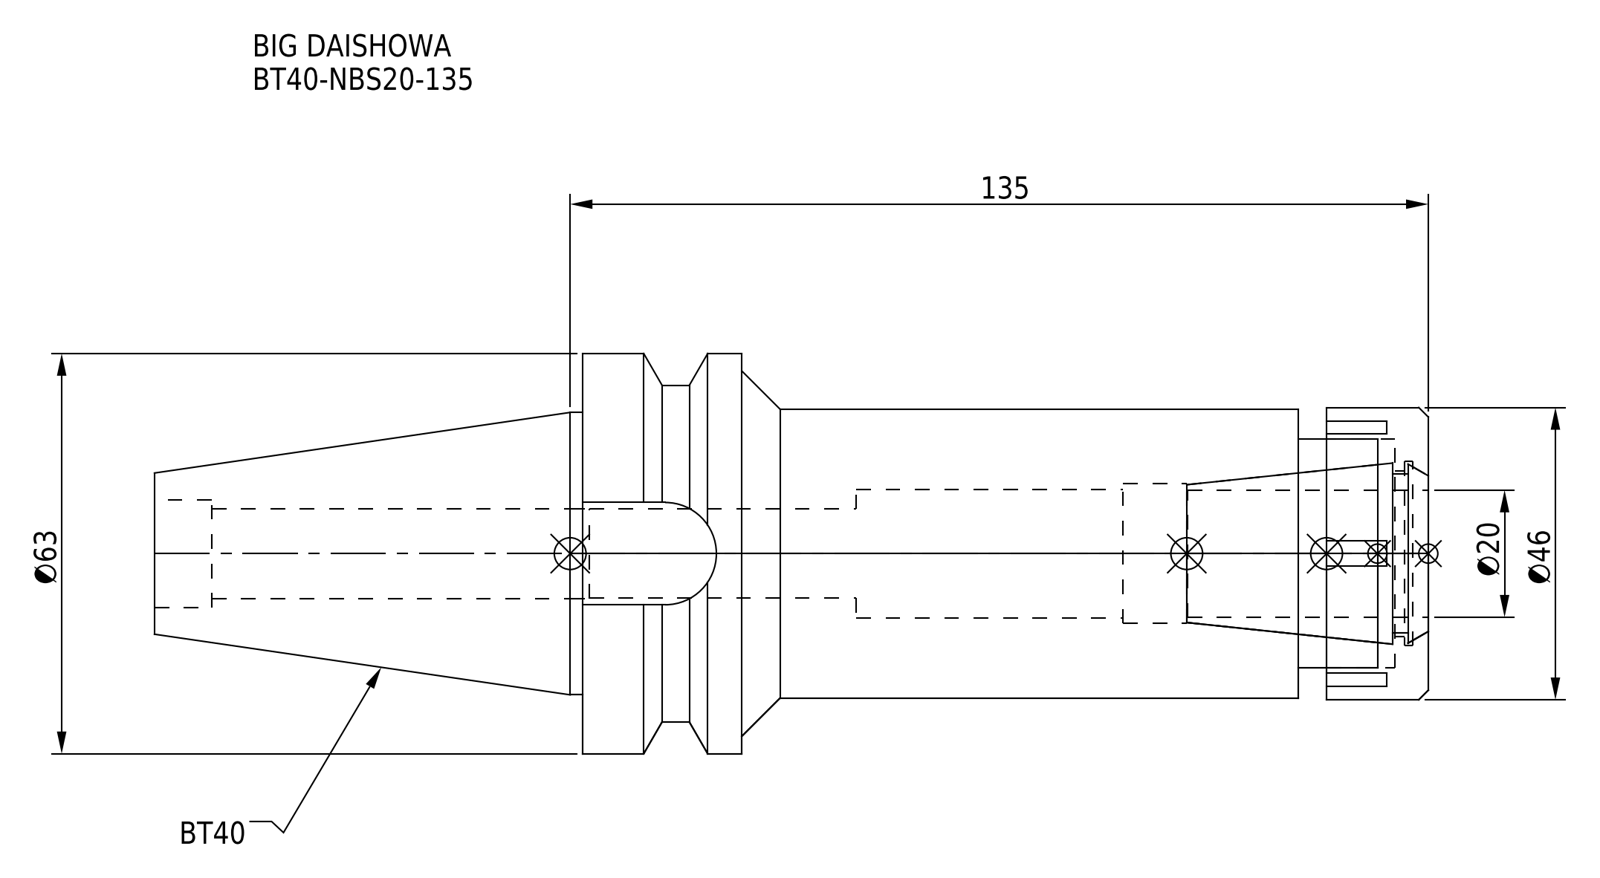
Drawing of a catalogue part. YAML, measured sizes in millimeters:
part_name: "BT40-NBS20-135.stp; BT40-NBS20-135; BT40-NBS20-135_1.stp; BT40NB20135-200_ASM.stp (+3 more)"
step_written_by: "SolidWorks 2019 (CONFIG_CONTROL_DESIGN)"
units: millimeters
bodies: {solids: 2, faces: 93, planar: 45, cylindrical: 34, other: 14}
overall_size: [200.4, 63, 63]
volume: 254002
surface_area: 49082
round_holes:
  - {diameter: 14, count: 1}
  - {diameter: 14.2, count: 1}
  - {diameter: 17, count: 1}
  - {diameter: 20.3, count: 1}
  - {diameter: 22, count: 1}
  - {diameter: 26, count: 1}
  - {diameter: 29, count: 1}
  - {diameter: 36, count: 1}
round_bosses_or_shafts:
  - {diameter: 63, count: 1}
  - {diameter: 53, count: 1}
  - {diameter: 46, count: 1}
  - {diameter: 45.5, count: 1}
  - {diameter: 44.45, count: 1}
partial_cylinders:
  - {radius: 8.05, count: 1}
face_to_face_distances: [133, 8, 20.5, 112.5, 87.5, 16, 4.5, 117, 108, 92]
